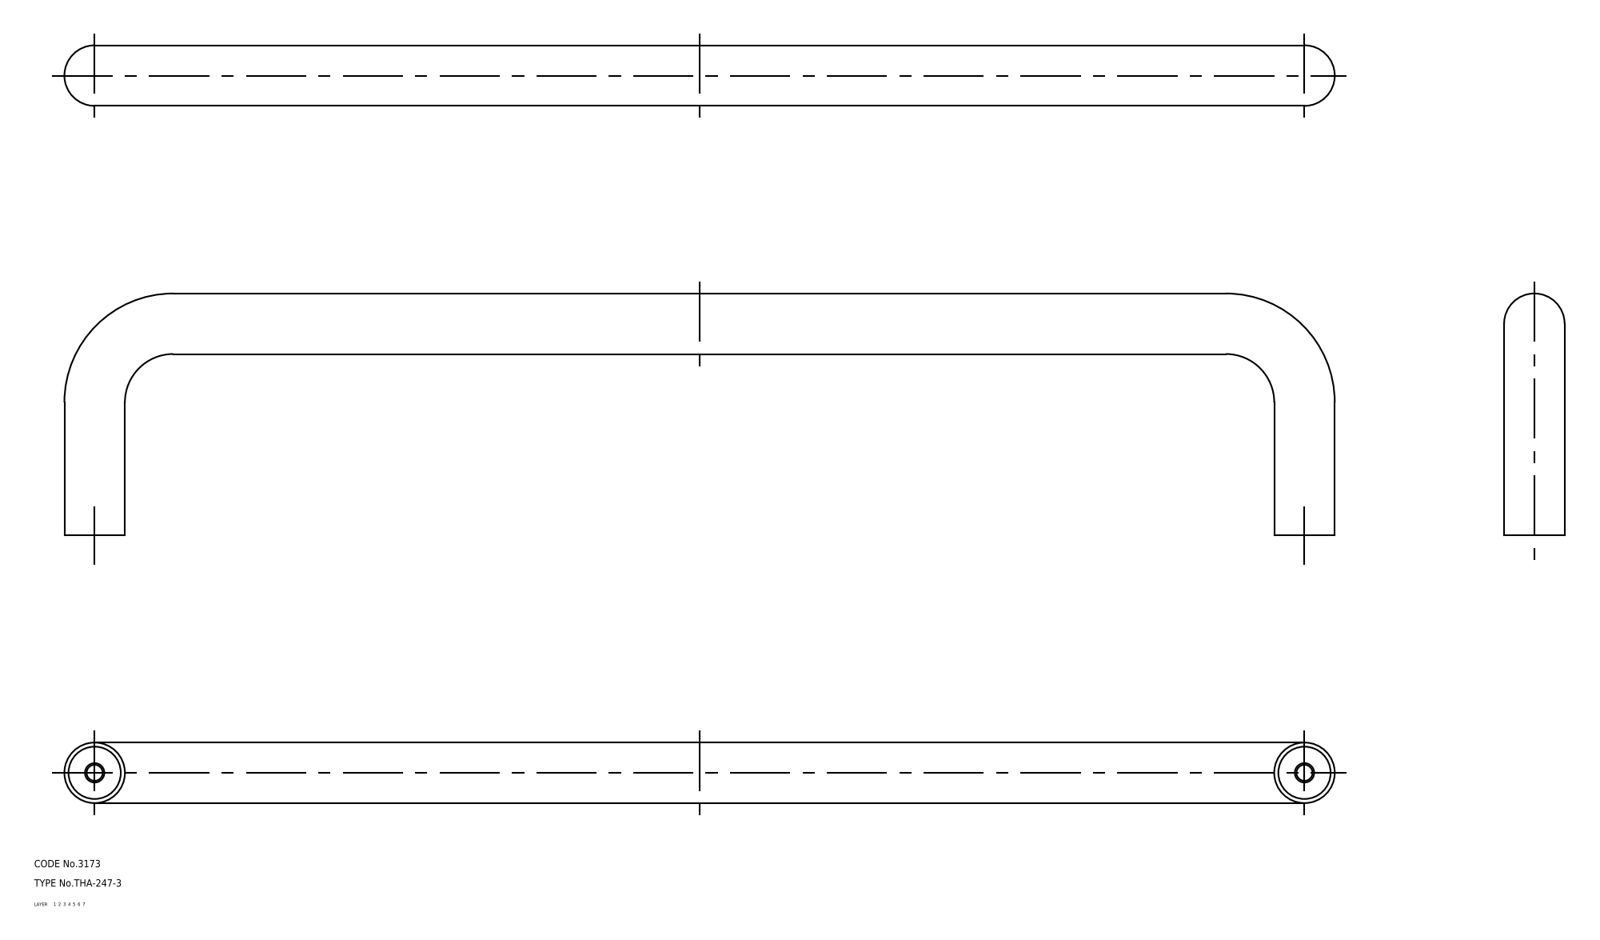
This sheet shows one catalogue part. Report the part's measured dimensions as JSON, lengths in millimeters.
{"part_name": "attachment; pull; THA_247_3_28136_36", "step_written_by": "CADfix (AUTOMOTIVE_DESIGN)", "units": "millimeters", "bodies": {"solids": 3, "faces": 34, "planar": 0, "cylindrical": 0, "other": 34}, "overall_size": [525, 100, 25], "volume_mm3": 92541, "surface_area_mm2": 99301}
